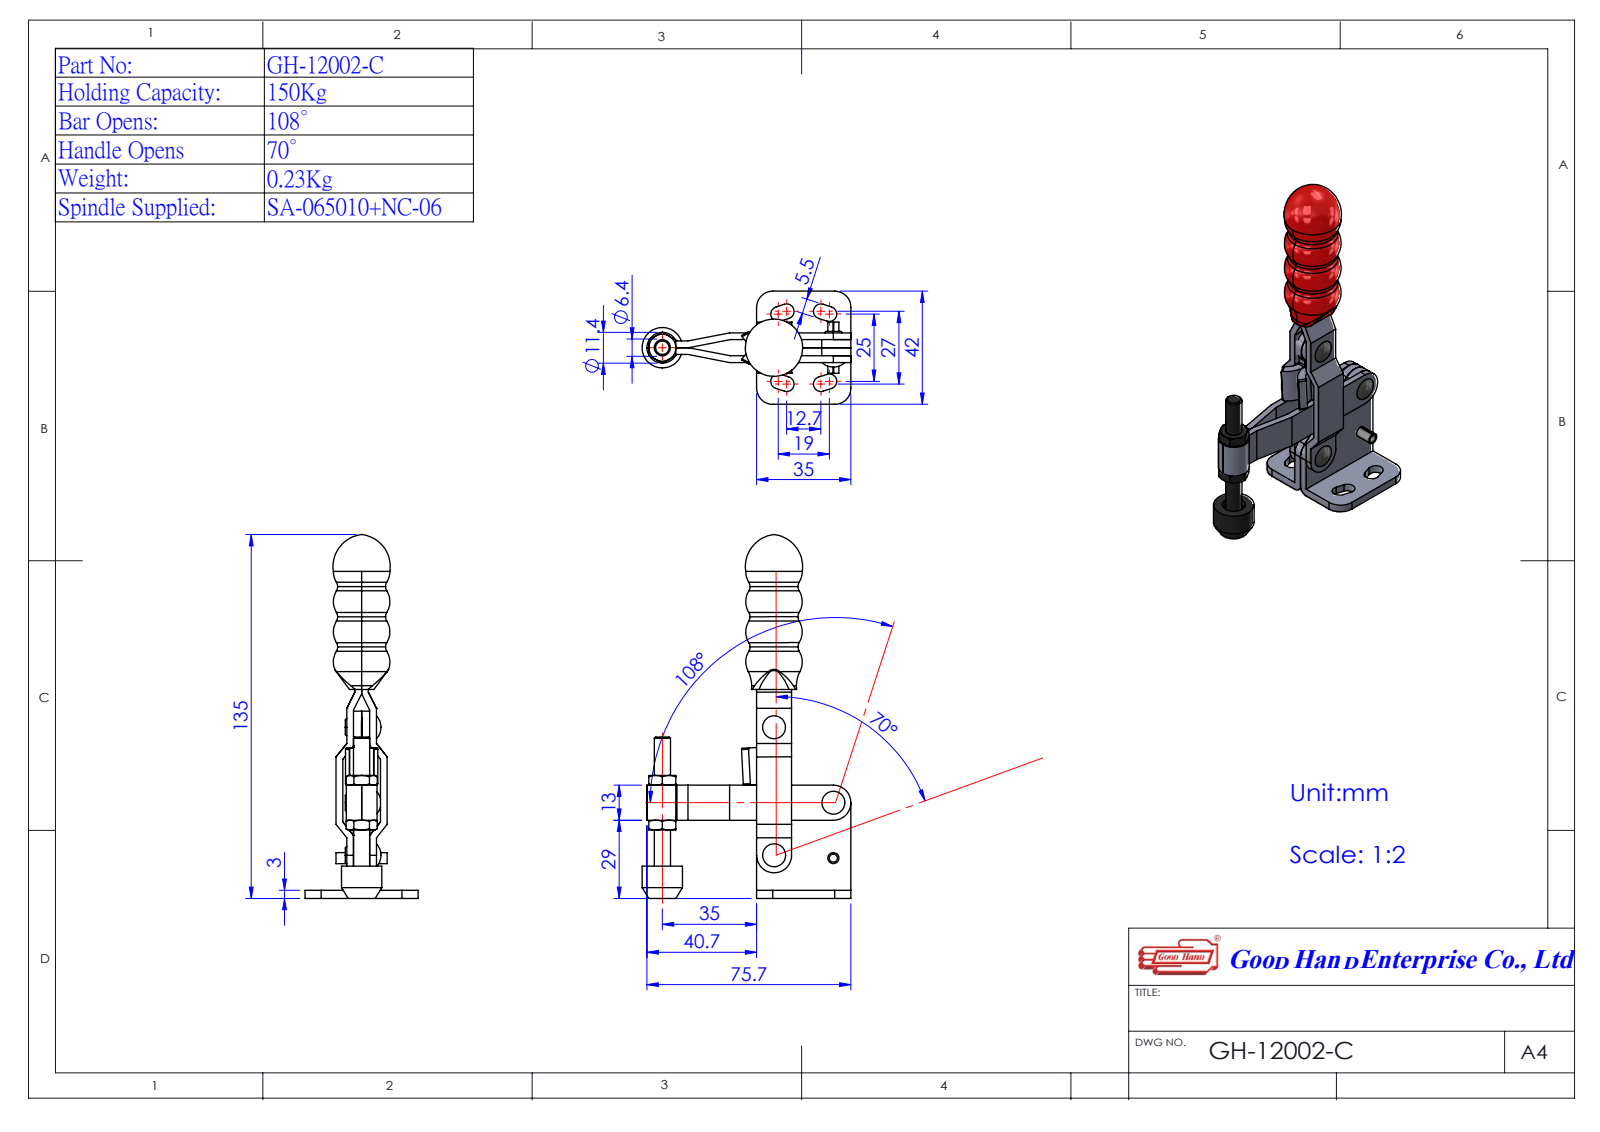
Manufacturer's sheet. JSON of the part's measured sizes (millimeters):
{"part_name": "Group4^GH-12002-C(簡化); Group3^GH-12002-C(簡化); Group4^GH-12002-C(簡化)-1; Group2^GH-12002-C(簡化)-1 (+2 more)", "step_written_by": "SolidWorks 2016 (AUTOMOTIVE_DESIGN)", "units": "millimeters", "bodies": {"solids": 5, "faces": 298, "planar": 116, "cylindrical": 104, "other": 78}, "overall_size": [135, 77.5, 42], "volume_mm3": 42785, "surface_area_mm2": 23260, "round_holes": [[3.5, 4], [4.05, 2], [6.4, 1]], "round_bosses_or_shafts": [[15, 1], [11.4, 1], [6, 1], [4.1, 1]], "partial_cylinders_radius": [[2.75, 8], [6, 8], [0.5, 4], [2, 4], [6.5, 3], [3, 2], [9, 2]], "face_to_face_distances": [2.5, 6, 8.5, 4, 12.5, 3, 13, 10, 11, 6.5], "hole_center_spacings": [19.56, 20.53, 28.04, 29.4, 35.63, 47.5]}
